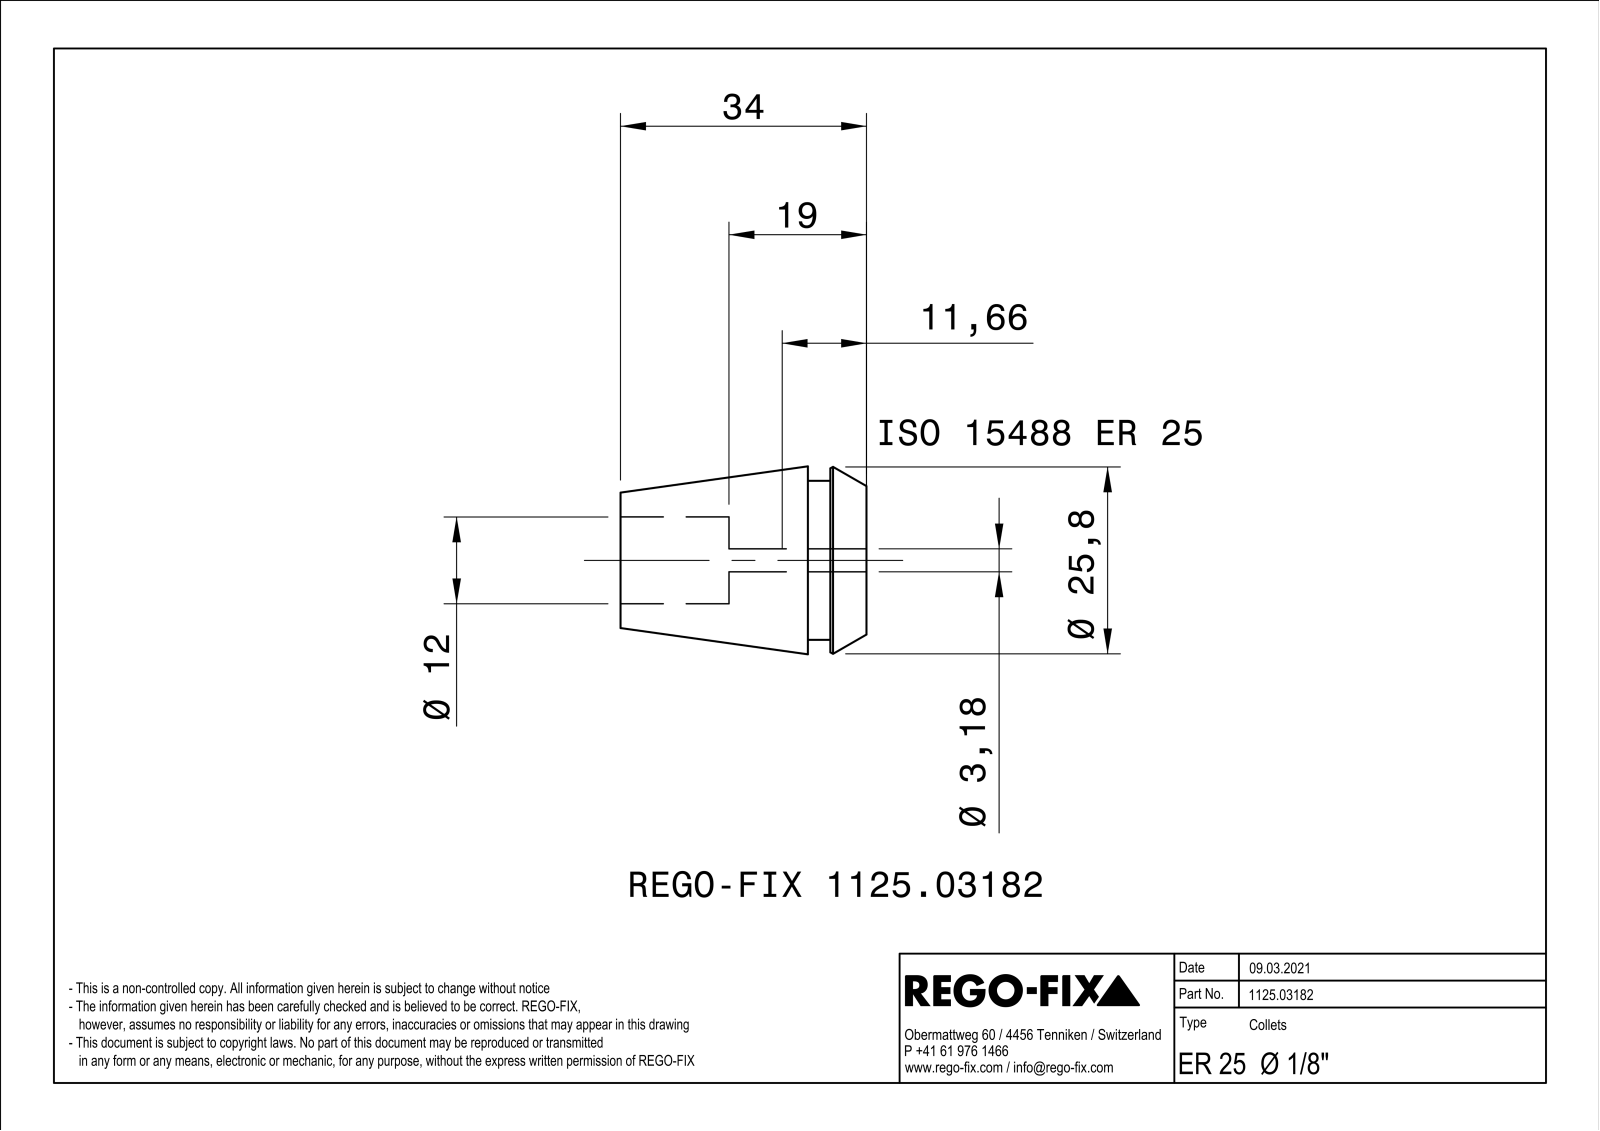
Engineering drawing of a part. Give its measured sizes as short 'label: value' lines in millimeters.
name: NOCUT
written by: SIEMENS PLM Software Solid Edge ST10 (AUTOMOTIVE_DESIGN)
unit: mm
bodies: 1 solid, 272 faces (104 planar, 48 cylindrical, 120 other)
size: 34 × 25.99 × 25.99
volume: 9 961 mm³; area: 9 462 mm²
holes: 1× ⌀12
bosses: 1× ⌀22
rounds: 8× R40, 1× R1.59
face distances: 0.6, 0.62, 0.58, 8.1, 34, 25.9, 5, 3.1, 29, 19
